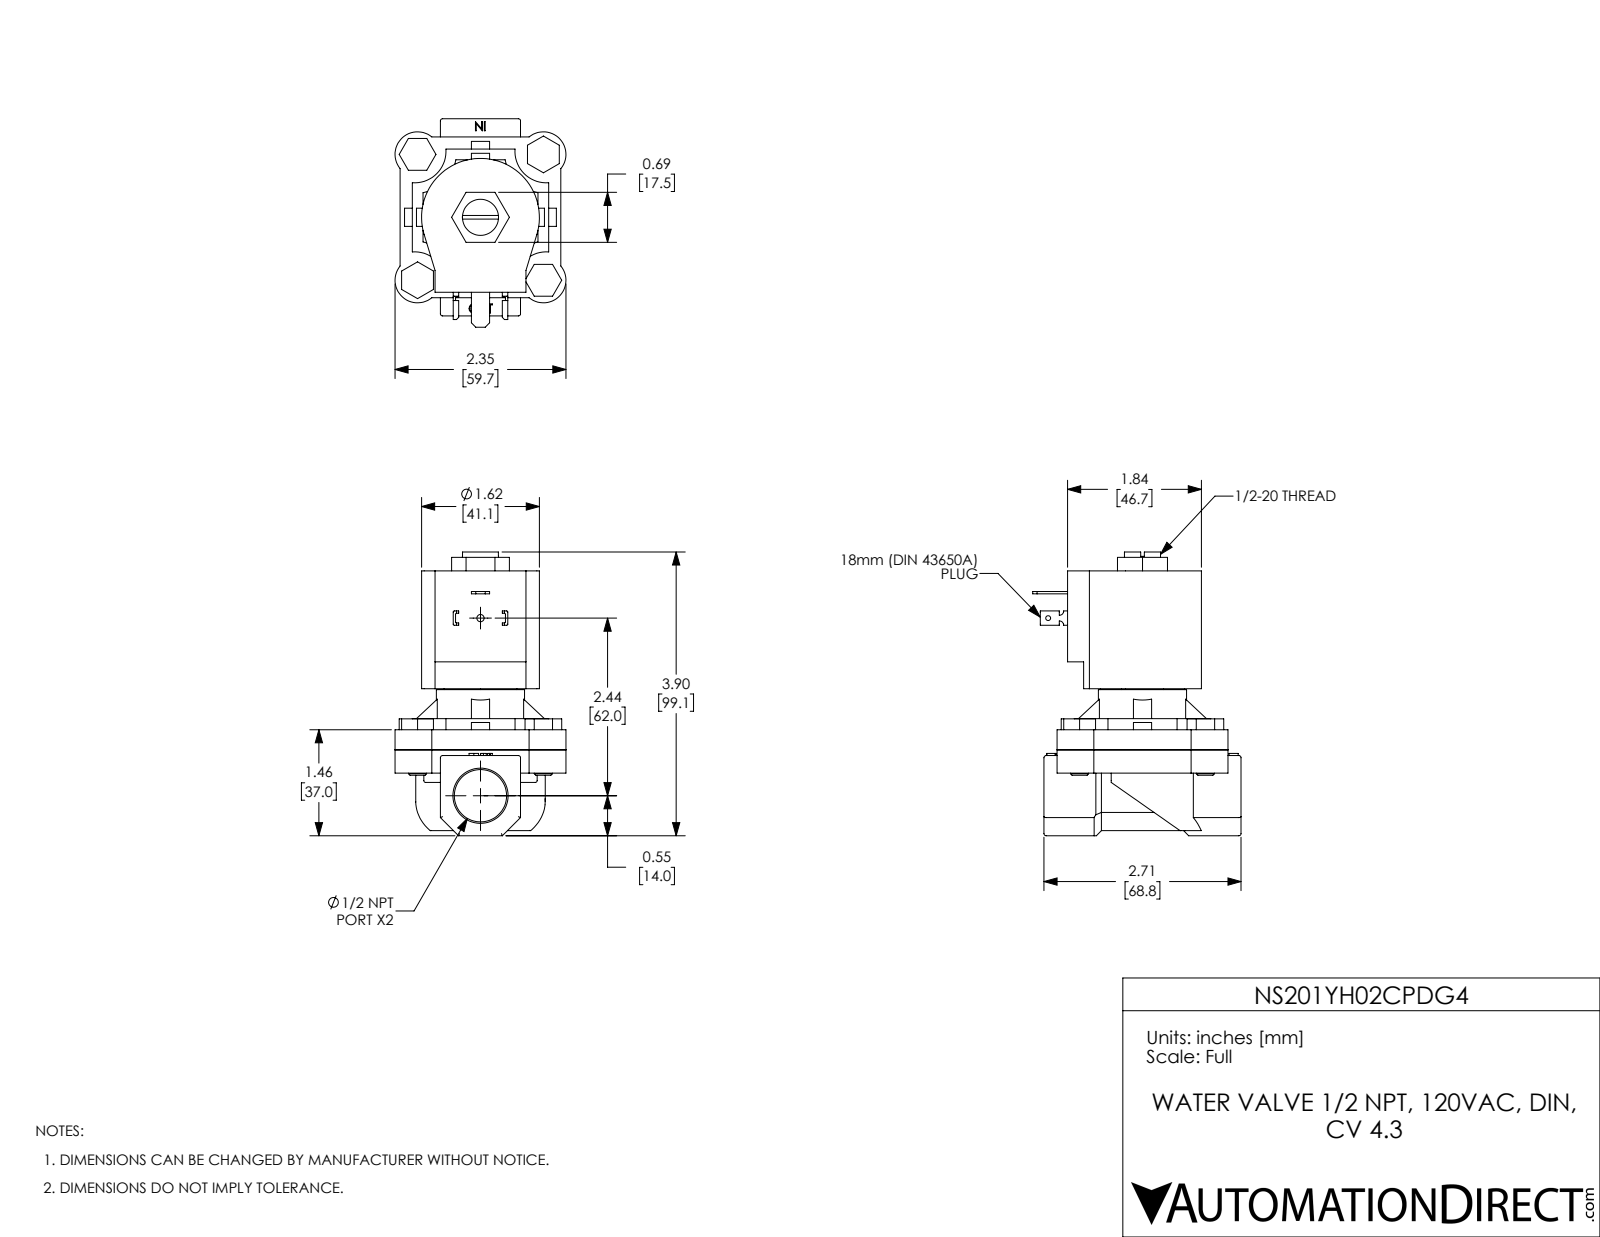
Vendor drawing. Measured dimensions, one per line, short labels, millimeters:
name: NS201YH02CPDG4
written by: SolidWorks 2024 (CONFIG_CONTROL_DESIGN)
unit: mm
bodies: 11 solids, 385 faces (239 planar, 113 cylindrical, 33 other)
size: 99.1 × 72.8 × 59.7
volume: 165 000 mm³; area: 43 540 mm²
holes: 4× ⌀6.4, 1× ⌀1.7, 1× ⌀2.5, 1× ⌀12.6, 1× ⌀13, 1× ⌀18.3, 1× ⌀29.3
bosses: 4× ⌀6.3, 1× ⌀30.8
rounds: 15× R0.8, 8× R0.4, 4× R7.9, 4× R11, 4× R14.7, 2× R1.5, 1× R20.6, 1× R22.6
face distances: 7, 62.5, 55.4, 8.1, 15.1, 70.6, 14.1, 42.1, 6.4, 28
hole spacings: 31.1, 43.9, 62.1, 62
